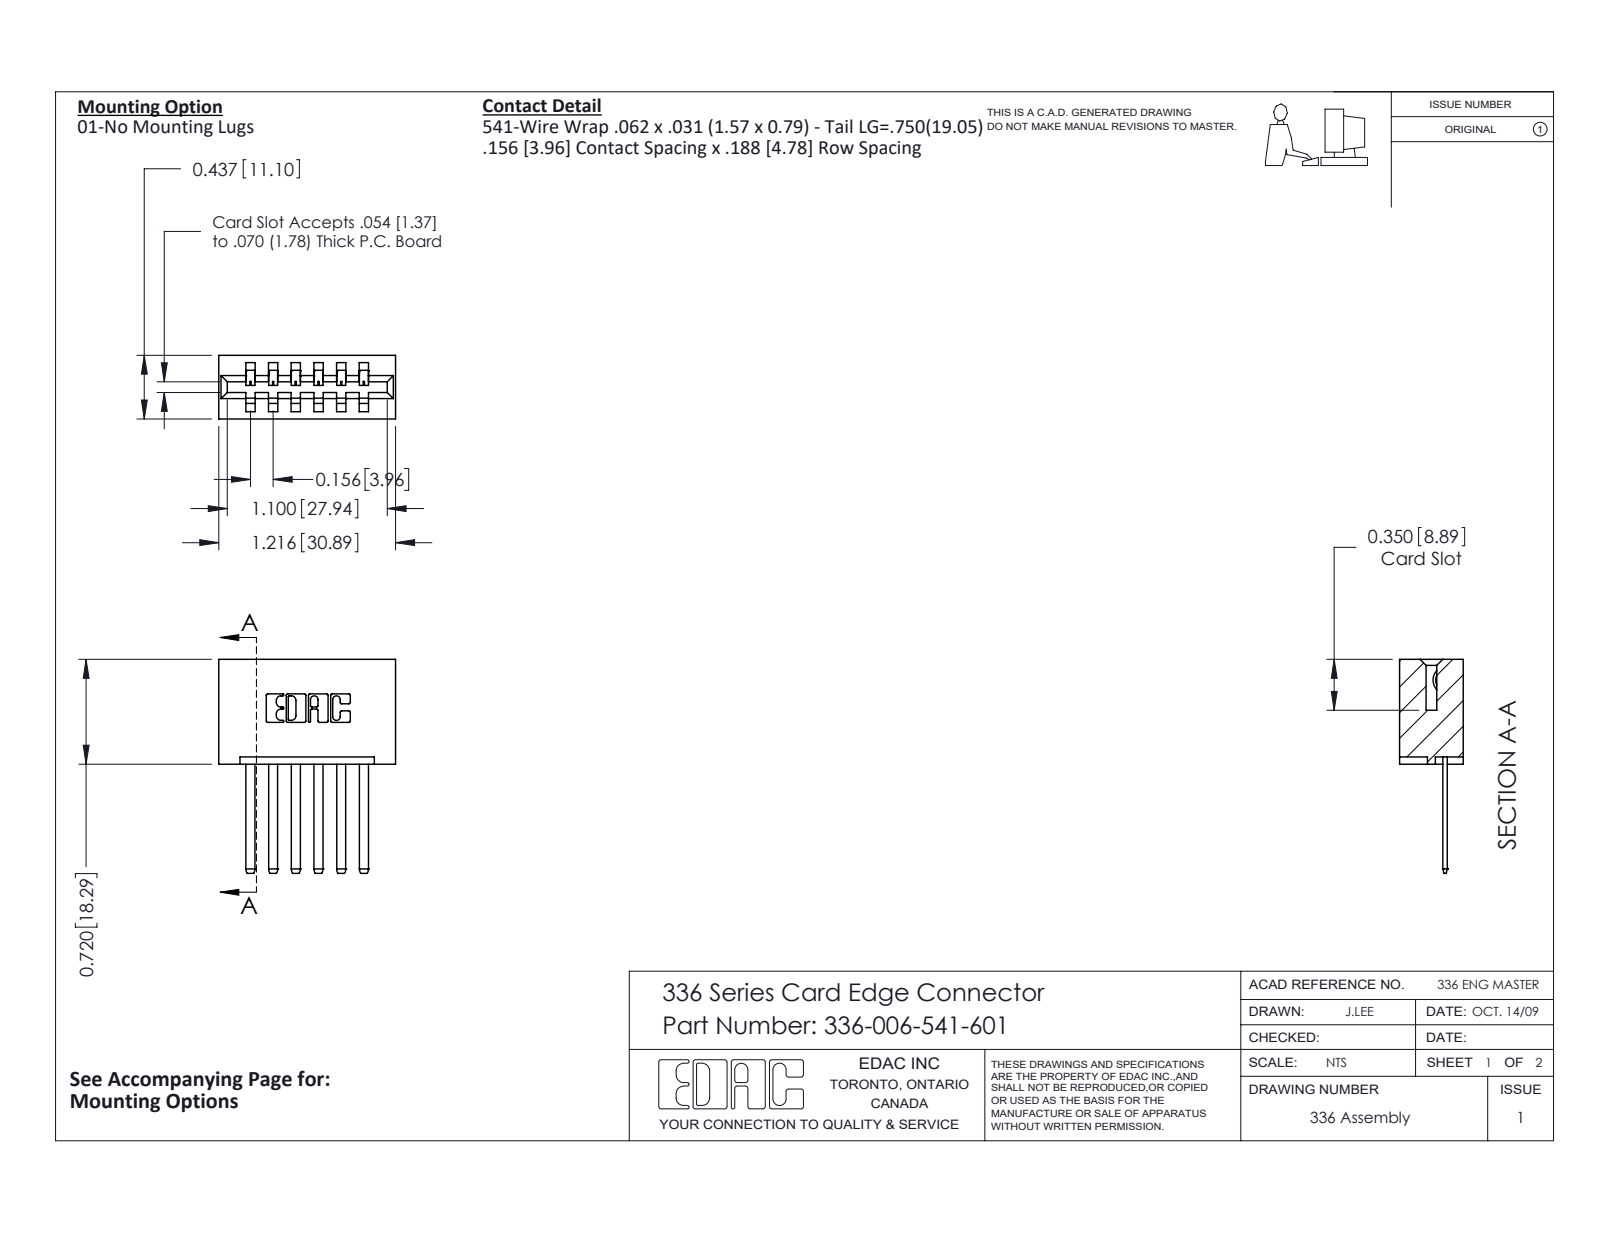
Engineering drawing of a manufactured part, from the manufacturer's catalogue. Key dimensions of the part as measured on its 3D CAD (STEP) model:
Part name (STEP PRODUCT): 336 Part_Lugless; 336-006-541-601; 336-290-001_336-290-541
STEP written by: SolidWorks 2020 (CONFIG_CONTROL_DESIGN)
Units: inches
Bodies: 7 solids, 406 faces (270 planar, 136 cylindrical, 0 other)
Overall size (bounding box): 1.47 × 1.216 × 0.437
Volume: 0.305 in³ · Surface area: 7.768 in²
Partial cylindrical surfaces — rounded edges, fillets, slot ends (radius × count): R0.01 ×22, R0.004 ×12, R0.056 ×12, R0.007 ×6, R0.031 ×6, R0.026 ×3, R0.022 ×2, R0.04 ×2
Main face-to-face distances: 0.156, 0.437, 0.312, 0.376, 0.22, 0.181, 0.05, 0.256, 0.312, 0.468
